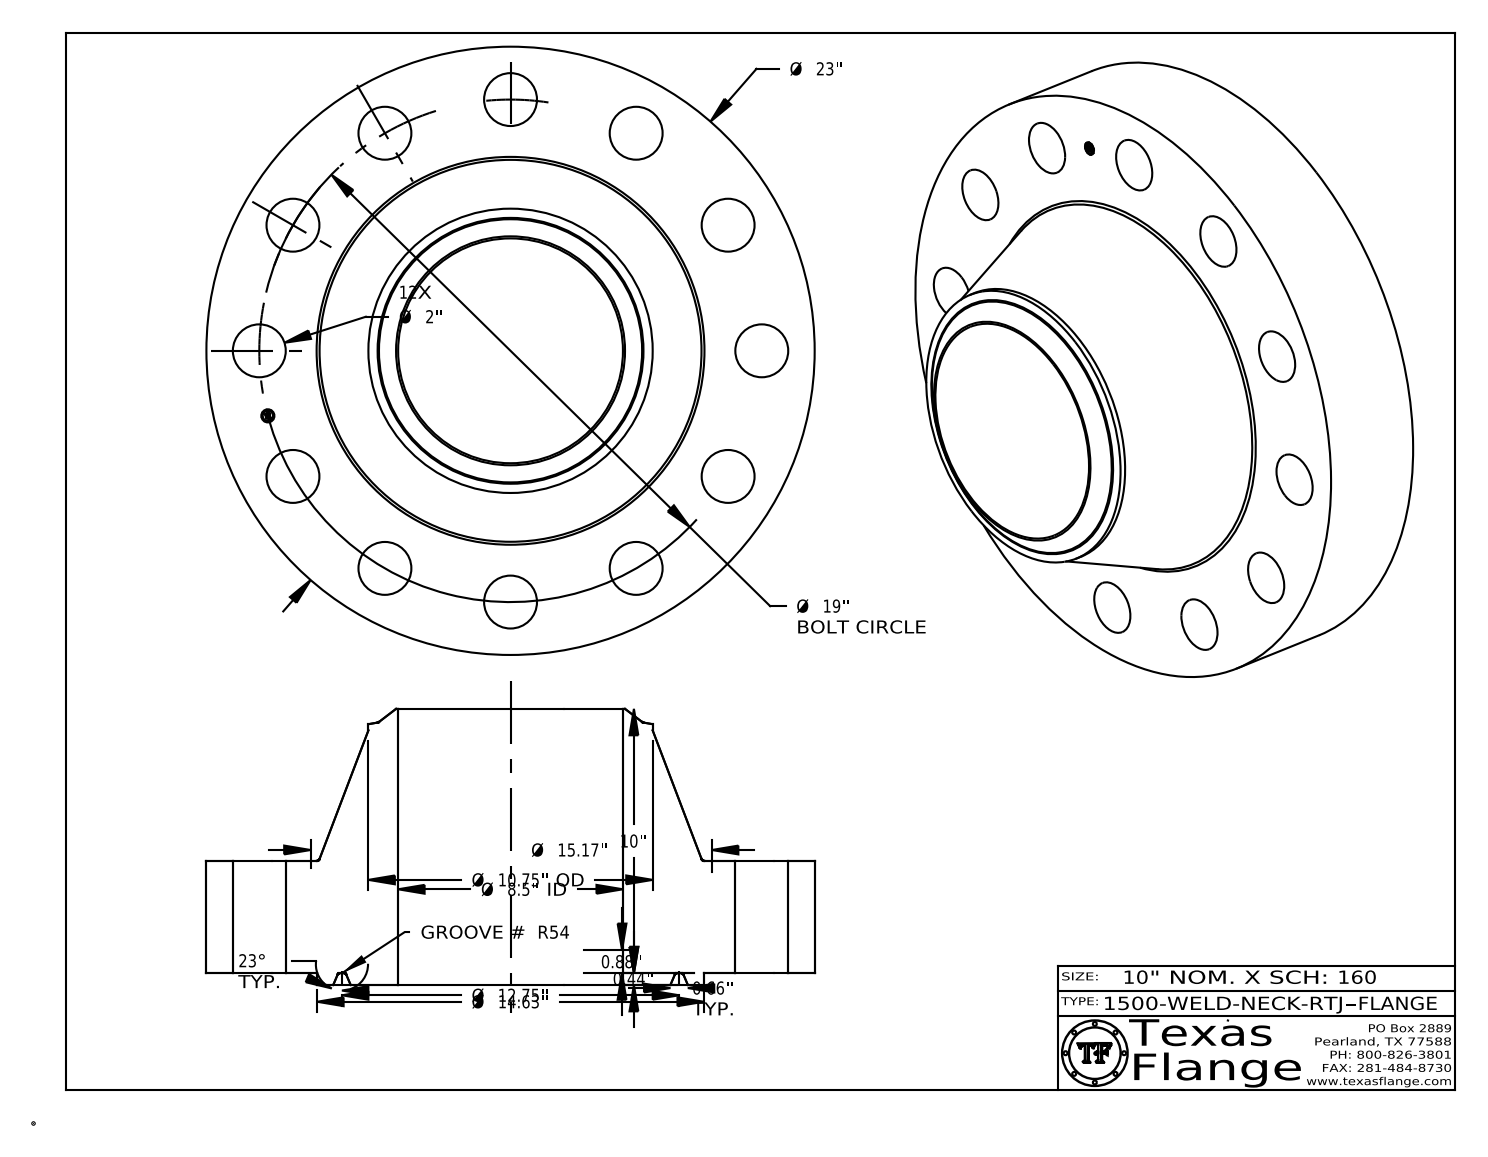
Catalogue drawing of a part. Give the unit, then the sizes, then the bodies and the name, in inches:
Units: inches
Overall size (bounding box): 23 × 23 × 10.438
Round holes (diameter × count): ⌀2 ×12, ⌀0.495 ×1, ⌀8.5 ×1
Round bosses / shafts (diameter × count): ⌀0.03 ×8, ⌀23 ×1, ⌀14.625 ×1, ⌀10.75 ×1, ⌀0.39 ×1
Main face-to-face distances: 4.25, 0.438, 4.688, 10.438, 10, 5.75, 4.673, 4.235, 0.015, 5.765
Hole centre spacings: 9.5, 13.435, 16.454, 18.352, 4.918, 19, 4.917, 15.074
Volume: 1 763 in³ · Surface area: 1 738 in²
Bodies: 1 solid, 441 faces (371 planar, 52 cylindrical, 18 other)
Part name (STEP PRODUCT): 1500-WELD-NECK-RTJ
STEP written by: CATIA V5 STEP AP214 (AUTOMOTIVE_DESIGN)
